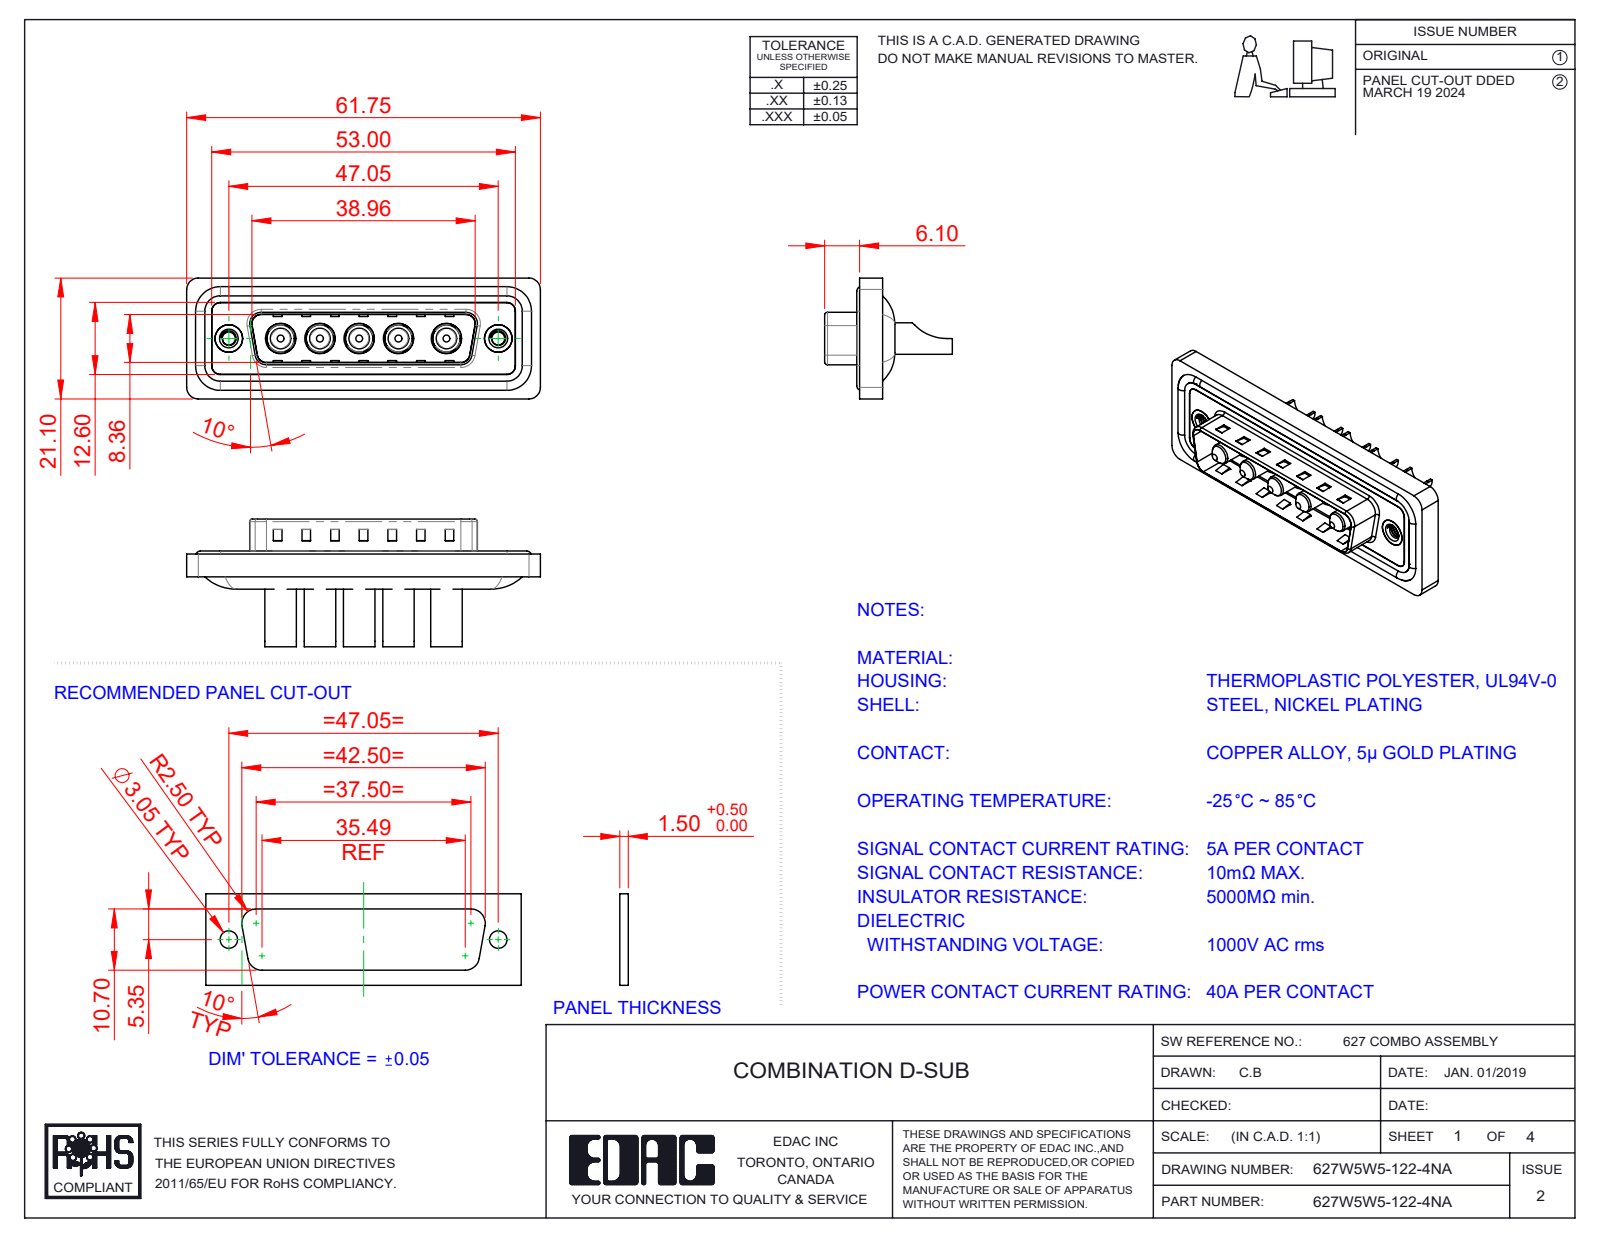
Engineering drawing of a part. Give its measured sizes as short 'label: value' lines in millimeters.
name: 627Combo Shell Rear_25 Contacts; 627Combo Shell Front_25 Contacts; 627Combo Housing_5W5; 627W5W5-122-4NA (+3 more)
written by: SolidWorks 2023 (CONFIG_CONTROL_DESIGN)
unit: mm
bodies: 17 solids, 691 faces (269 planar, 290 cylindrical, 132 other)
size: 61.75 × 22.3 × 21.1
volume: 7 674 mm³; area: 12 493 mm²
holes: 5× ⌀4.6, 5× ⌀4.85, 5× ⌀5.3, 2× ⌀2.26, 2× ⌀4, 2× ⌀4.8, 2× ⌀5
bosses: 5× ⌀5.5, 5× ⌀5.2, 5× ⌀4.75, 5× ⌀3.75, 5× ⌀3.6, 4× ⌀1.6, 2× ⌀4.9
rounds: 22× R1.5, 18× R2, 8× R0.5, 8× R1.6, 5× R2.1, 4× R0.25, 4× R0.6, 4× R0.65
face distances: 0.4, 0.5, 1.1, 1.5, 3.1, 1.6, 2.9, 0.82, 9.58, 5.65
hole spacings: 6.86, 9.04, 13.73, 38.01, 6.87, 8.37, 8.38, 9.05
